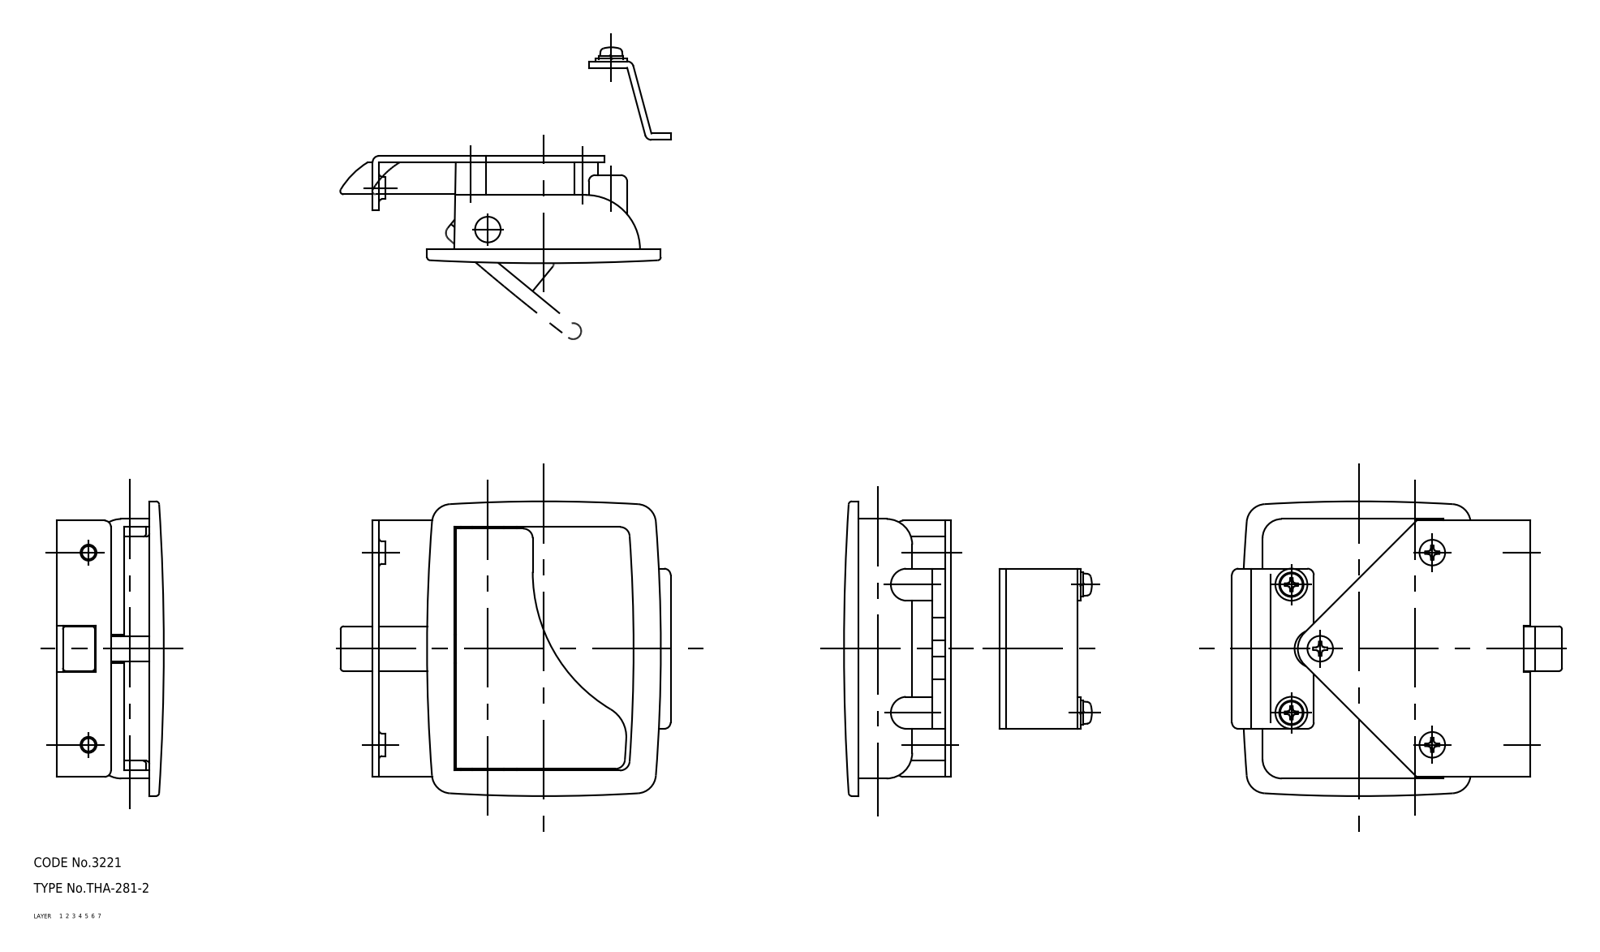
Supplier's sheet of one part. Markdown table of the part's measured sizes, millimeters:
| quantity | value |
| --- | --- |
| part name | bracket_B; screw; handle; base (+3 more) |
| STEP written by | CADfix (AUTOMOTIVE_DESIGN) |
| units | millimeters |
| bodies | 7 solids, 456 faces (0 planar, 0 cylindrical, 456 other) |
| overall size | 103.42 × 92 × 34.04 |
| volume | 68 357 mm³ |
| surface area | 54 018 mm² |
